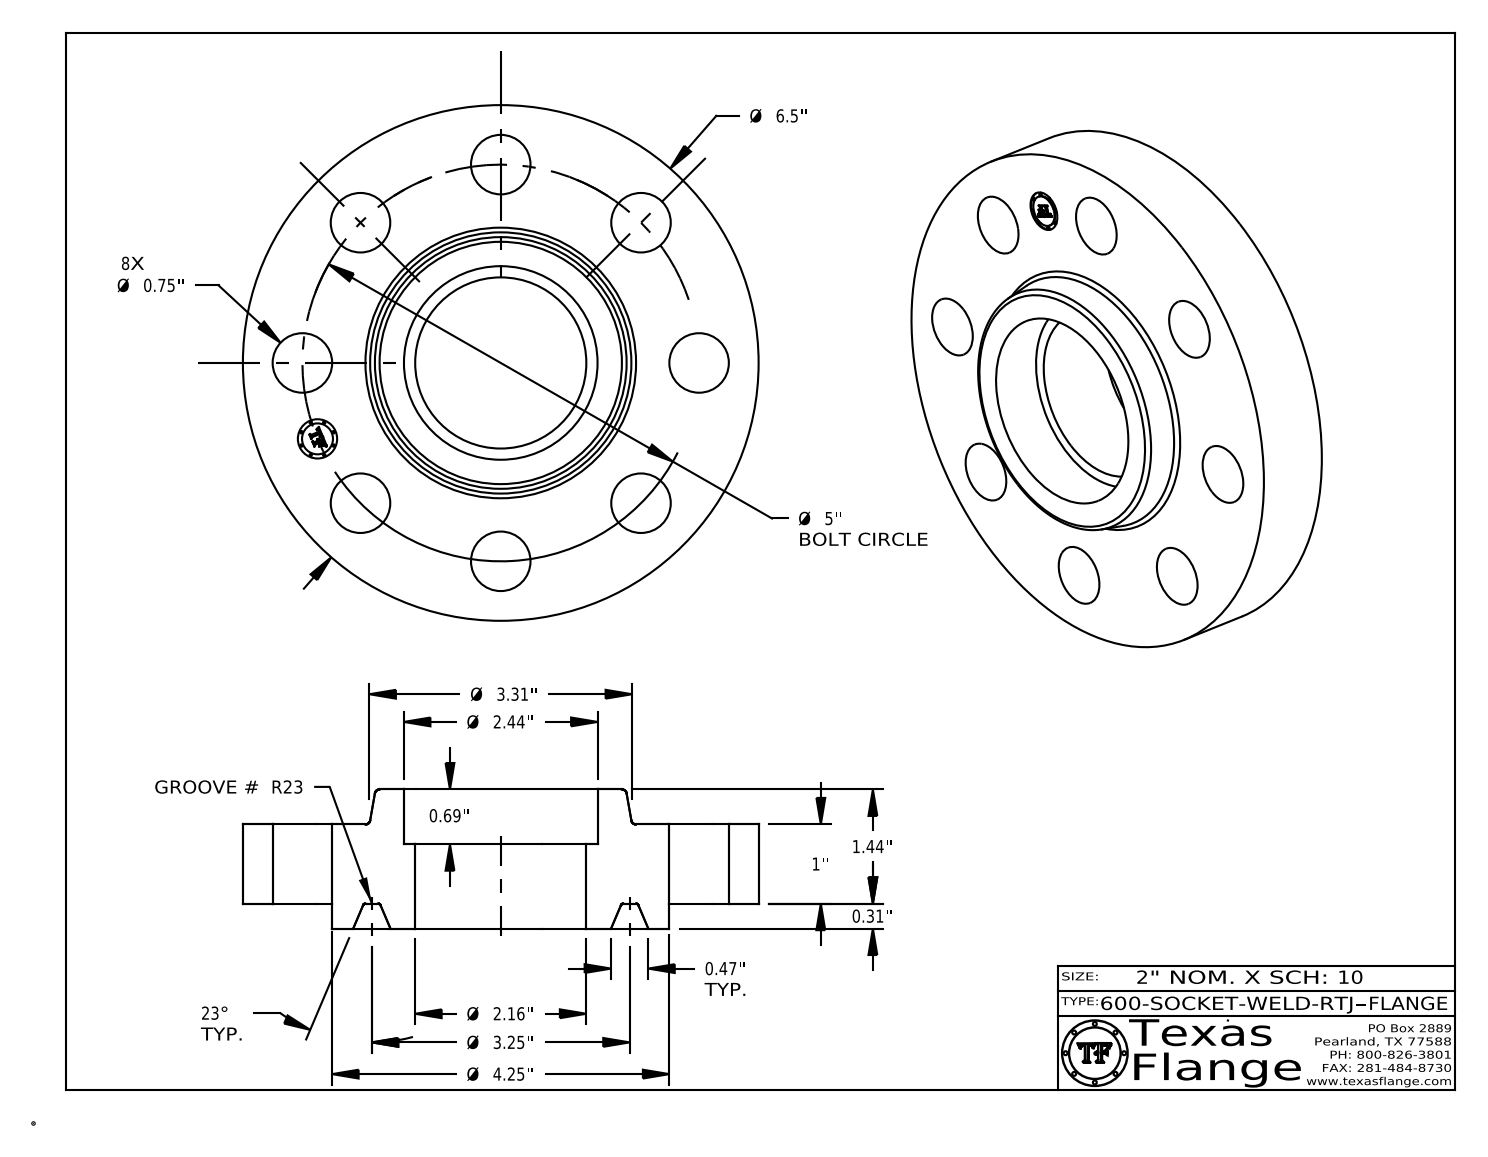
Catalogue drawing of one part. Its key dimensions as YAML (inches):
part_name: "600-SOCKET-WELD-RTJ"
step_written_by: "CATIA V5 STEP AP214 (AUTOMOTIVE_DESIGN)"
units: inches
bodies: {solids: 1, faces: 430, planar: 372, cylindrical: 44, other: 14}
overall_size: [6.5, 6.5, 1.753]
volume: 29.52
surface_area: 115.6
round_holes:
  - {diameter: 0.75, count: 8}
  - {diameter: 0.495, count: 1}
  - {diameter: 2.157, count: 1}
  - {diameter: 2.44, count: 1}
round_bosses_or_shafts:
  - {diameter: 0.03, count: 8}
  - {diameter: 6.5, count: 1}
  - {diameter: 4.25, count: 1}
  - {diameter: 0.39, count: 1}
face_to_face_distances: [1, 0.313, 1.313, 1.753, 1.44, 0.44, 1.063, 0.75, 0.25, 0.69]
hole_center_spacings: [2.5, 1.913, 3.535, 4.619, 5, 0.976, 2.778, 4.157]
